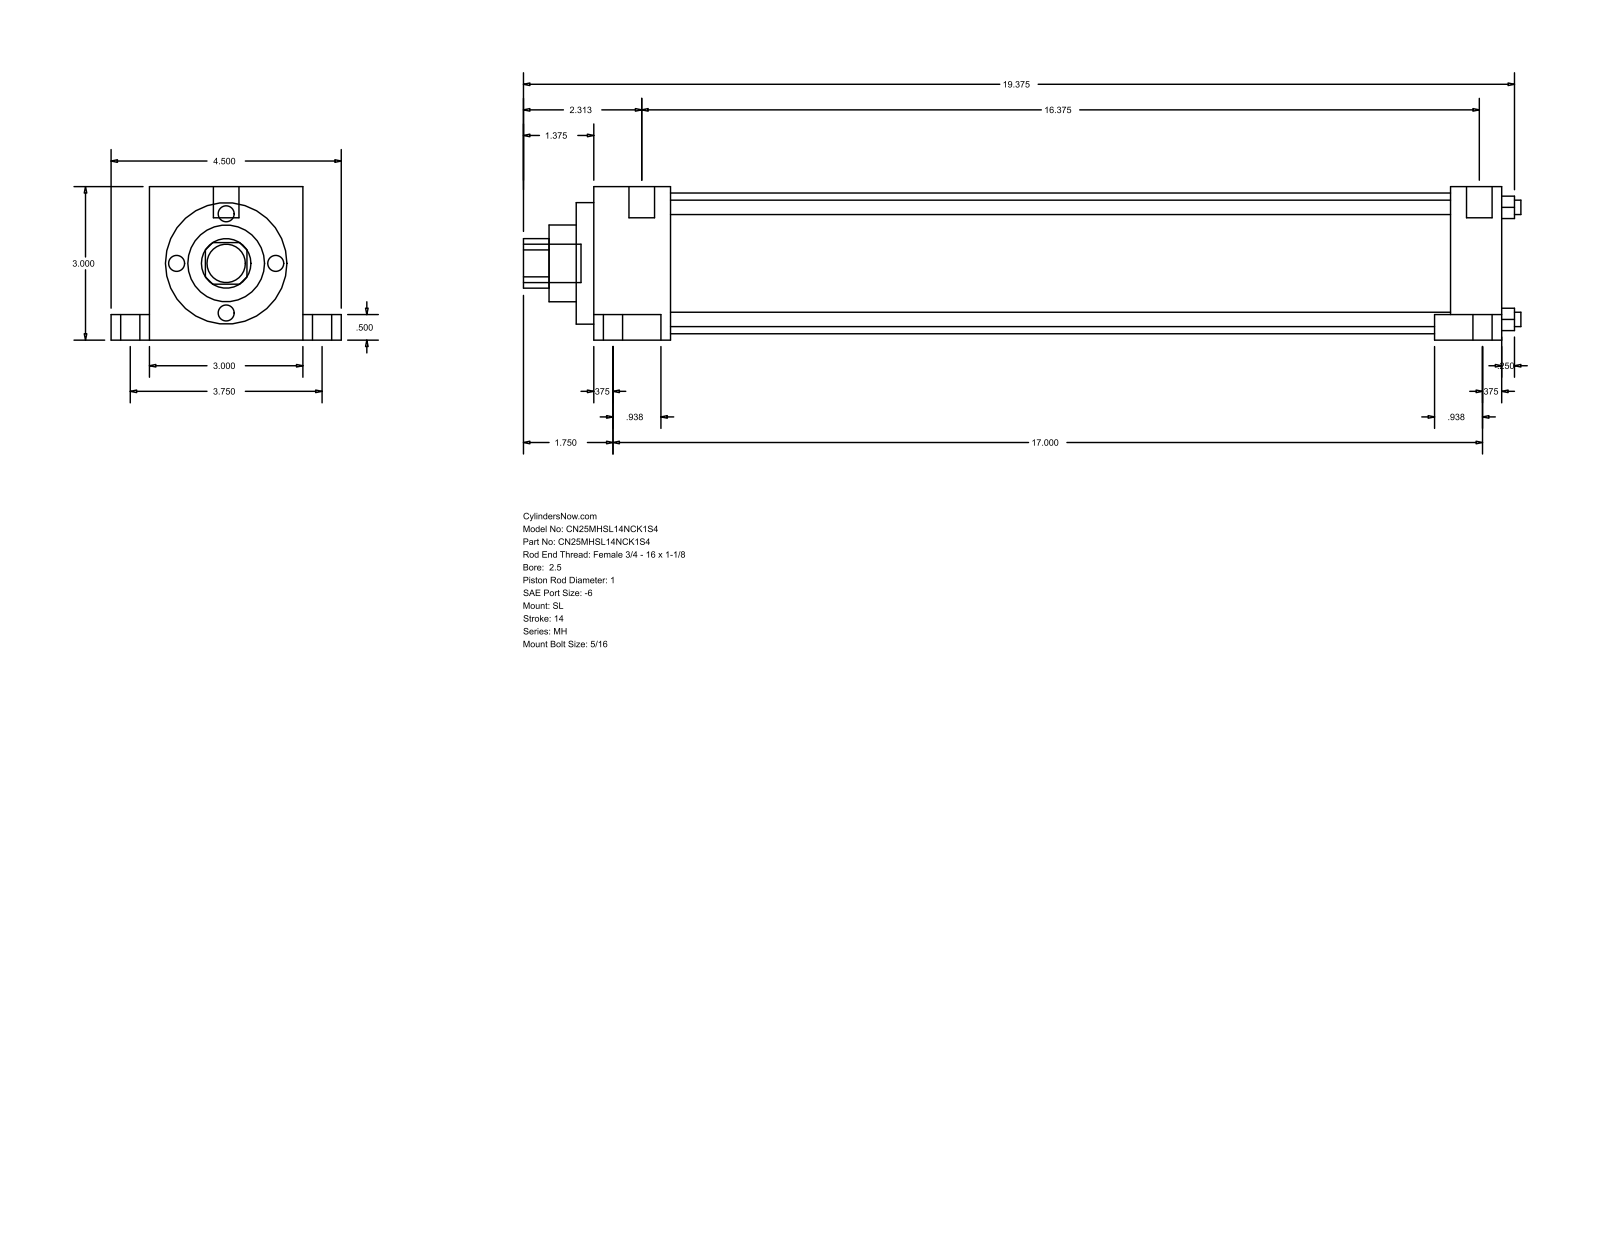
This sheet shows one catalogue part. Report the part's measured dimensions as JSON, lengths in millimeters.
{"part_name": "MH_SL__0250_1", "step_written_by": "GSSL Pune (CONFIG_CONTROL_DESIGN)", "units": "millimeters", "bodies": {"solids": 0, "faces": 86, "planar": 61, "cylindrical": 25, "other": 0}, "overall_size": [495.3, 114.3, 76.2], "round_holes": [[7.14, 4], [25.4, 1], [38.1, 1], [60.33, 1], [69.85, 1]], "round_bosses_or_shafts": [[15.88, 2], [9.53, 2], [5.56, 2], [19.05, 1], [12.7, 1]], "partial_cylinders_radius": [[12.29, 1]], "face_to_face_distances": [76.2, 25.39, 434.19, 459.58, 12.7, 63.5, 19.05, 95.25, 13.49, 447.68], "hole_center_spacings": [39.33, 55.62, 78.66]}
